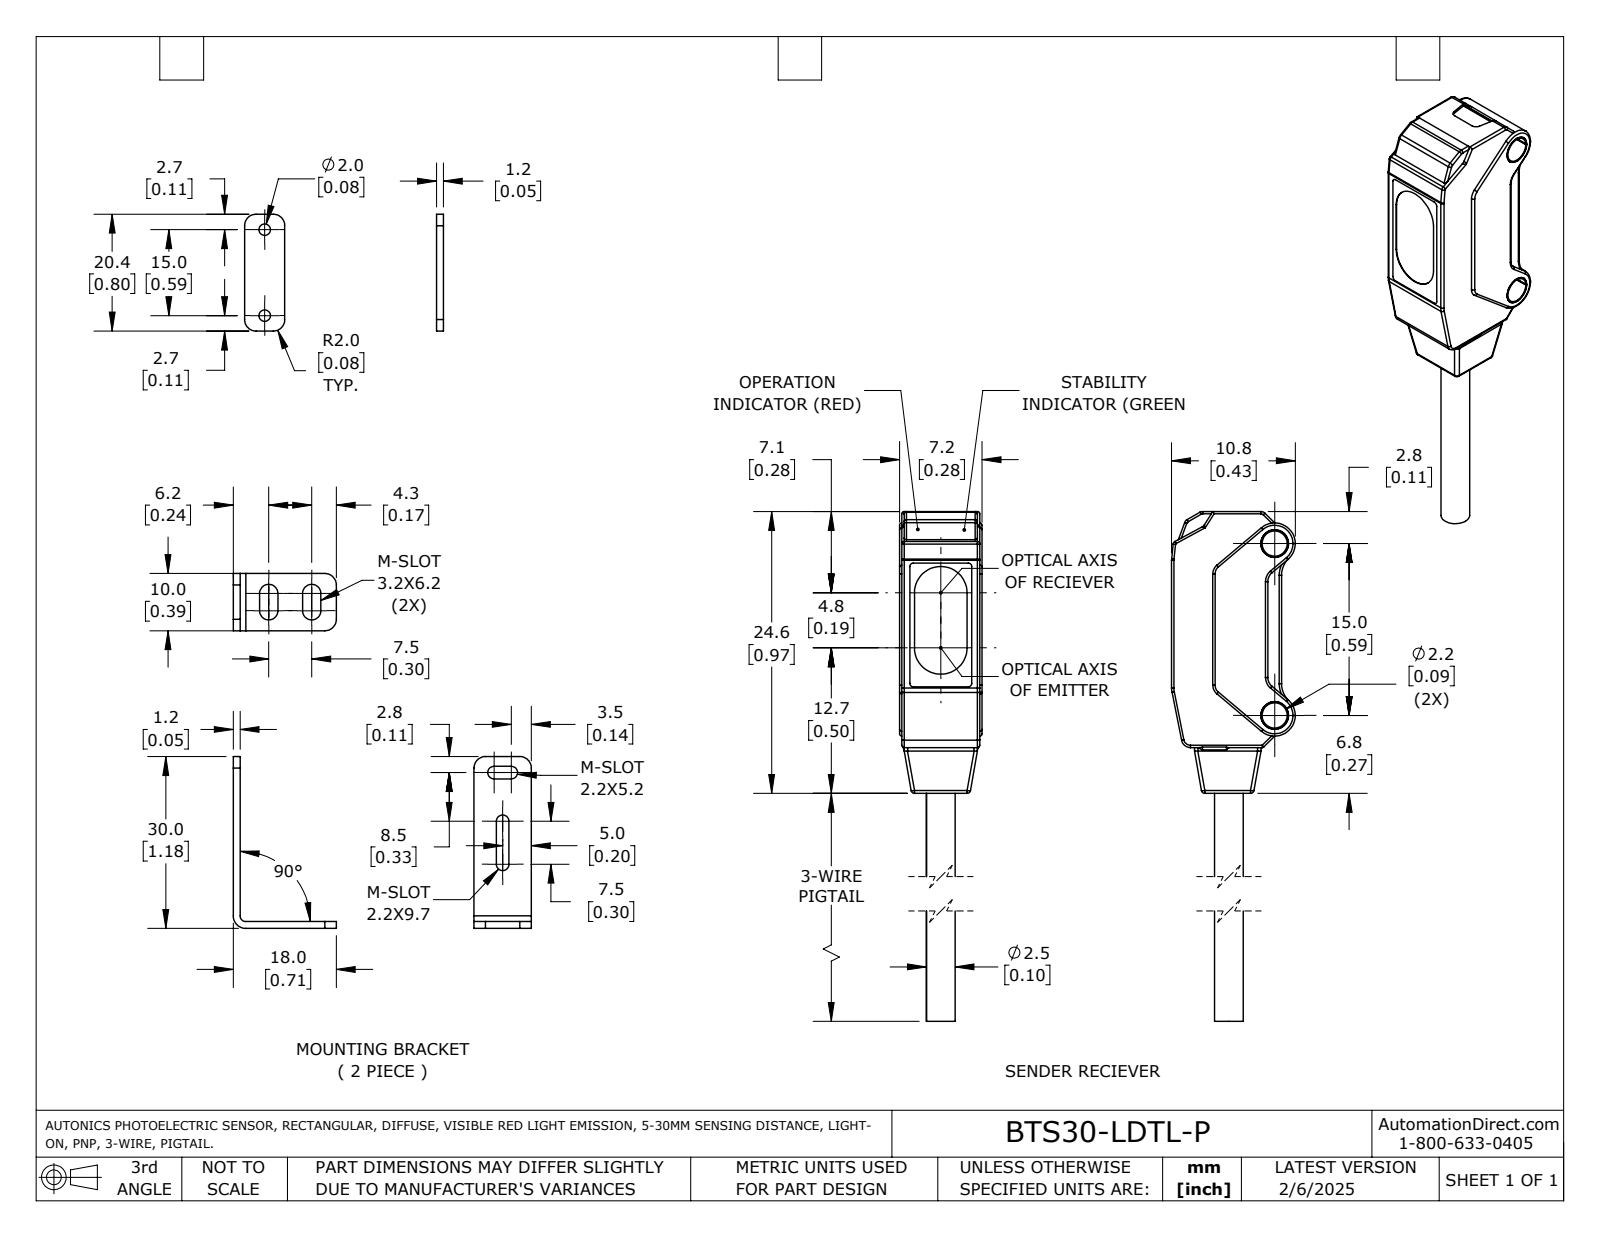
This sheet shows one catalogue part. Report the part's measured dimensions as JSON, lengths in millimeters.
{"part_name": "BTS15-LDTL_BTS15-LDTL-P_BTS15-LDTD_BTS15-LDTD-P_BTS30-LDTL_(3)", "step_written_by": "SolidWorks 2018 (AUTOMOTIVE_DESIGN)", "units": "millimeters", "bodies": {"solids": 5, "faces": 622, "planar": 404, "cylindrical": 144, "other": 74}, "overall_size": [41.68, 28.8, 14], "volume_mm3": 2243, "surface_area_mm2": 2664, "round_holes": [[2, 2], [2.2, 2], [2.41, 2]], "round_bosses_or_shafts": [[4, 2], [2.4, 2], [2.5, 1]], "partial_cylinders_radius": [[0.2, 39], [0.3, 14], [2, 11], [0.5, 6], [0.2, 5], [1.1, 4], [1.6, 4], [0.45, 2]], "face_to_face_distances": [1.2, 8.4, 7, 7.2, 8.2, 1.4, 9.6, 6.8, 5.6, 10], "hole_center_spacings": [15]}
